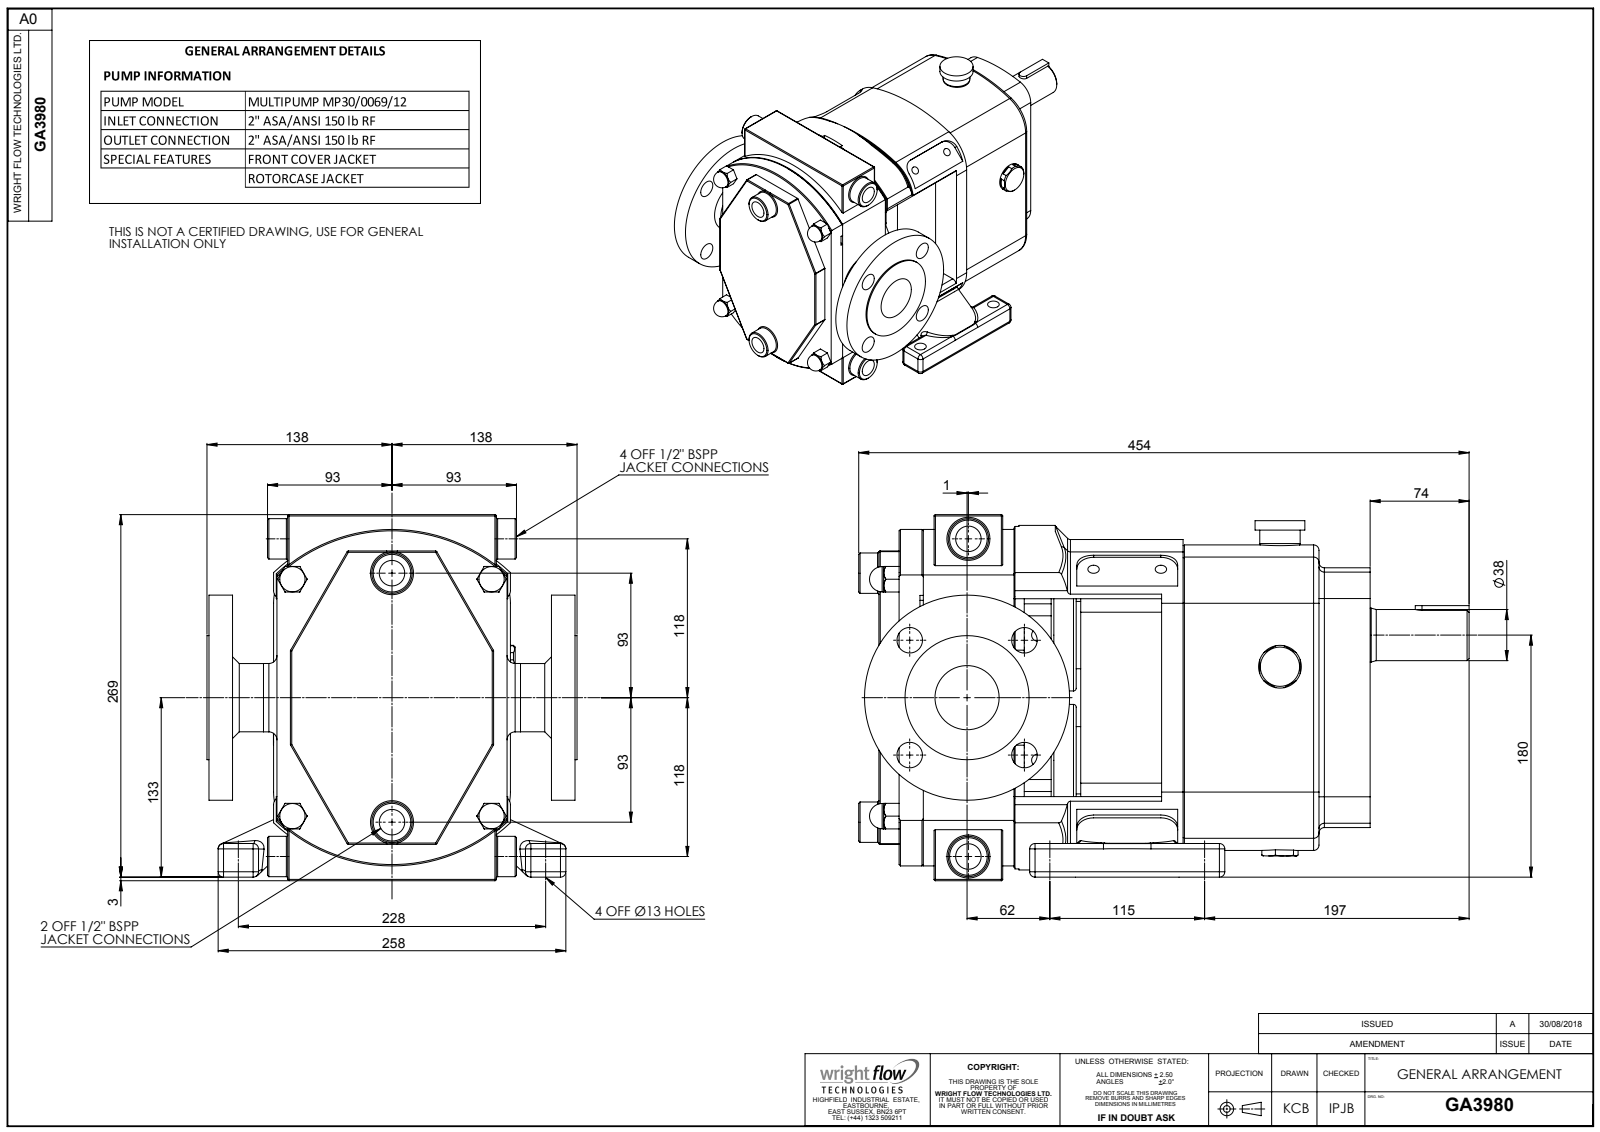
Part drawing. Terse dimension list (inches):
name: GA3980; Copy of Z94-5301-33 - 2 INCH ASA 150^GA3980; Copy of CP30-0069-12 H T^GA3980; Copy of MP30S Half Inch Jacket^GA3980 (+1 more)
written by: SolidWorks 2023 (AUTOMOTIVE_DESIGN)
unit: in
bodies: 6 solids, 870 faces (295 planar, 318 cylindrical, 257 other)
size: 17.857 × 10.827 × 10.709
volume: 777.4 in³; area: 1 143 in²
holes: 6× ⌀0.748, 4× ⌀0.335, 4× ⌀0.398, 4× ⌀0.512, 4× ⌀0.747, 2× ⌀0.358, 1× ⌀1.378, 1× ⌀1.878
bosses: 5× ⌀1.181, 4× ⌀0.74, 2× ⌀3.268, 2× ⌀1.969, 1× ⌀6, 1× ⌀3.63, 1× ⌀2, 1× ⌀1.996
rounds: 44× R0.039, 44× R0.157, 12× R0.394, 10× R0.236, 4× R0.492, 4× R0.495, 4× R0.496, 4× R0.787
face distances: 0.059, 1.299, 2.047, 8.72, 8.031, 1.358, 7.972, 6.673, 0.591, 1.201
hole spacings: 3.357, 2.374, 2.374, 5.133, 0.417, 1.372, 1.97, 2.505
